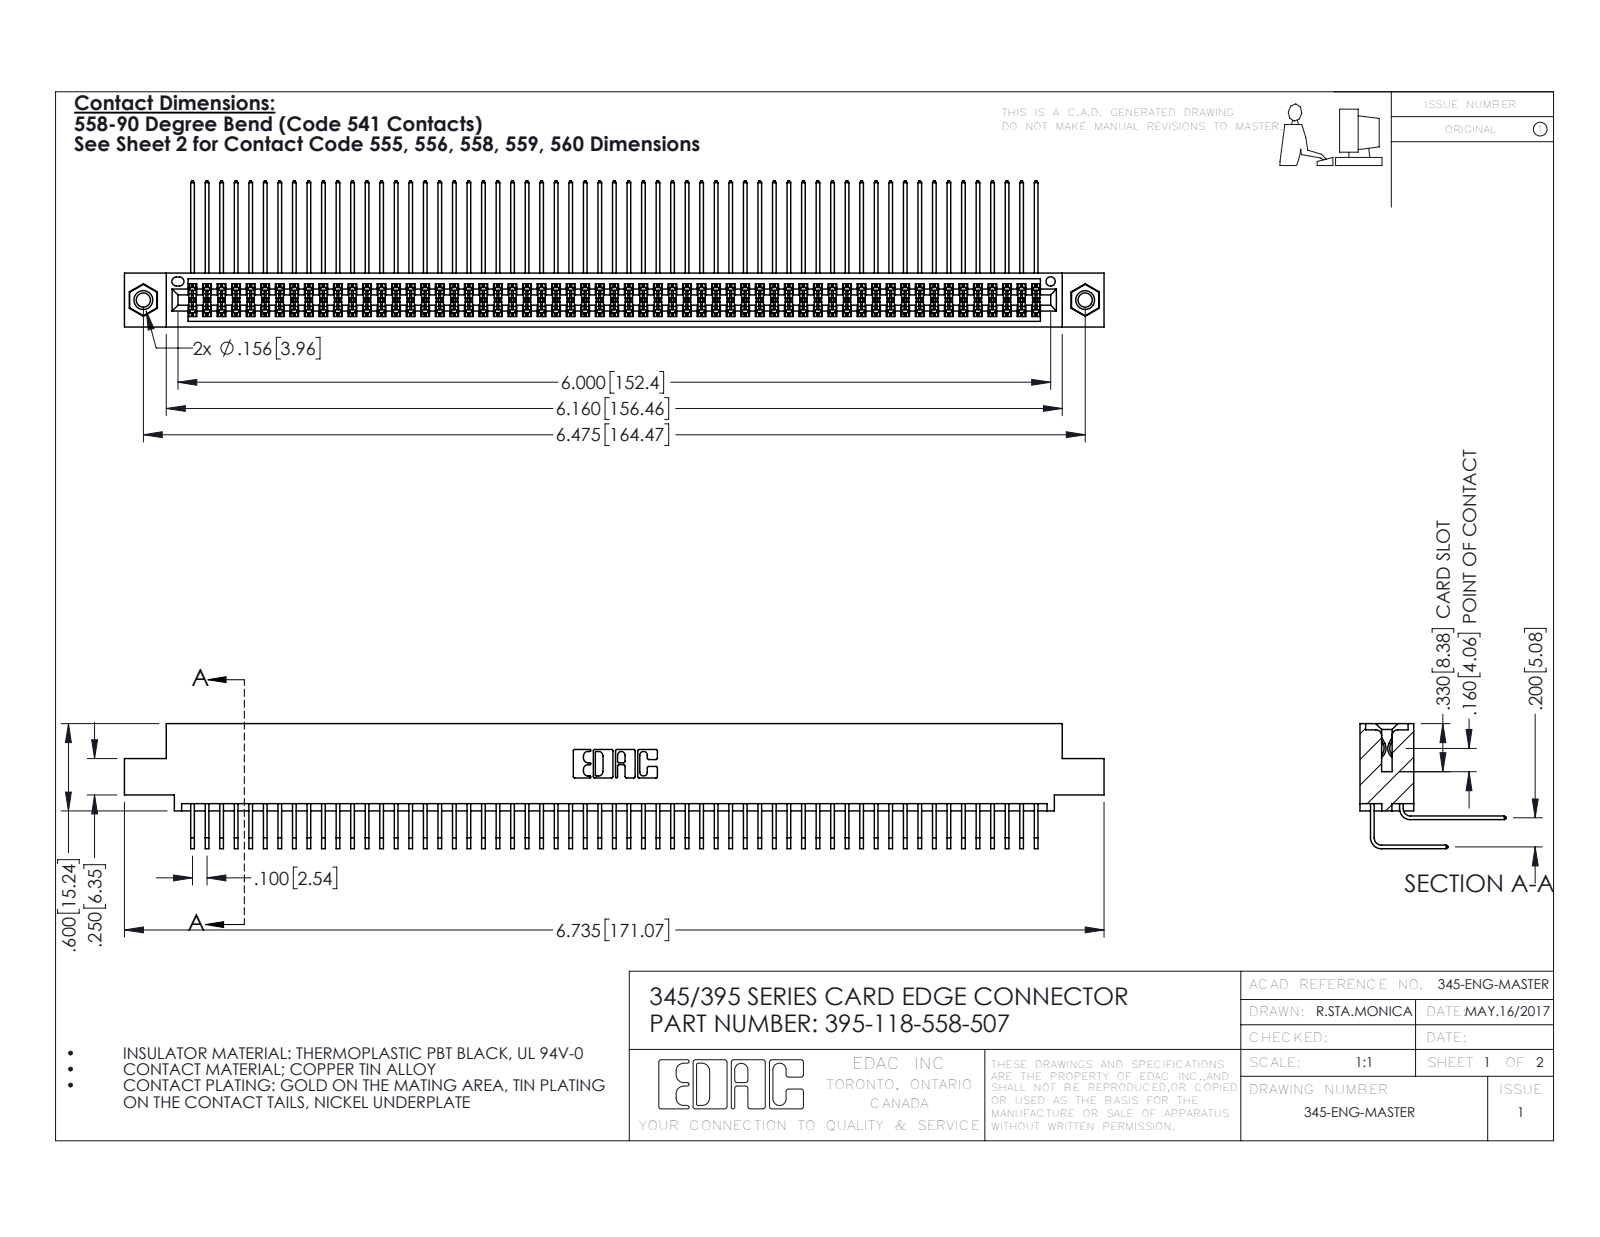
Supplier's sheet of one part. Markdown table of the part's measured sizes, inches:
| quantity | value |
| --- | --- |
| part name | 395-118-558-507; 345-250-001_345-250-005-103; 345-292-001_558 Tail - 2; 345-292-001_558 559 Tail - 1 (+1 more) |
| STEP written by | SolidWorks 2016 (CONFIG_CONTROL_DESIGN) |
| units | inches |
| bodies | 121 solids, 6326 faces (4246 planar, 2064 cylindrical, 16 other) |
| overall size | 6.735 × 1.005 × 0.859 |
| volume | 1.06 in³ |
| surface area | 45.46 in² |
| round holes (diameter × count) | 0.098 × 2, 0.125 × 2, 0.156 × 2, 0.064 × 1 |
| round bosses / shafts (diameter × count) | 0.155 × 2 |
| partial cylindrical surfaces (radius × count) | 0.006 × 178, 0.01 × 22, 0.007 × 6, 0.031 × 6, 0.026 × 3, 0.014 × 2, 0.019 × 2, 0.022 × 2 |
| main face-to-face distances | 0.072, 0.298, 0.2, 0.37, 0.098, 0.272, 0.025, 0.225, 0.025, 0.175 |
| hole center spacings | 0.27, 6.239, 6.475 |
